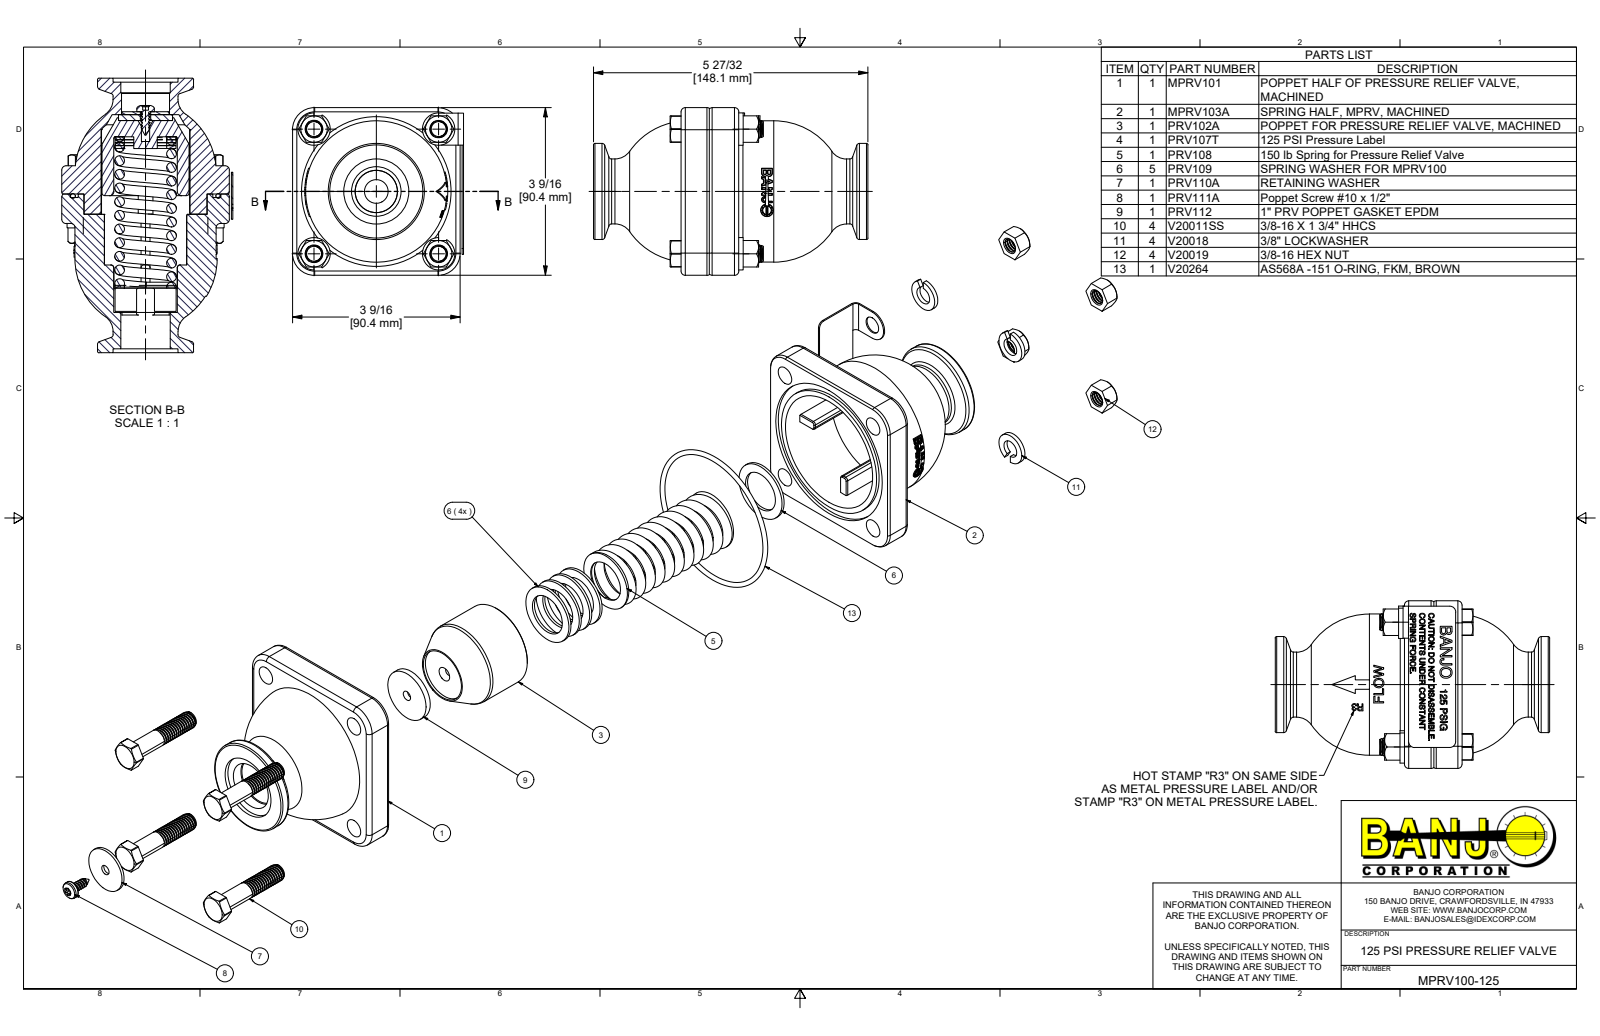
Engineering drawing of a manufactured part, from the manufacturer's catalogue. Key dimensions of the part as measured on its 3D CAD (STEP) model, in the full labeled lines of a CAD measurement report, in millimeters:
Part name (STEP PRODUCT): MPRV100-125; MPRV101; MPRV101X; MPRV103A (+8 more)
STEP written by: Autodesk Inventor 2022 (AUTOMOTIVE_DESIGN)
Units: millimetres
Bodies: 26 solids, 2572 faces (999 planar, 620 cylindrical, 953 other)
Overall size (bounding box): 148.1 × 92.3 × 90.4
Volume: 356 900 mm³ · Surface area: 152 700 mm²
Round holes (diameter × count): ⌀7.8 ×4, ⌀9.8 ×4, ⌀10.3 ×4, ⌀4.4 ×1, ⌀4.6 ×1, ⌀5.6 ×1, ⌀6.5 ×1, ⌀9.7 ×1, ⌀22.9 ×1, ⌀25.9 ×1, ⌀26.7 ×1, ⌀29.1 ×1
Round bosses / shafts (diameter × count): ⌀8.2 ×60, ⌀17.4 ×4, ⌀9.5 ×4, ⌀76.2 ×1, ⌀72.6 ×1, ⌀51.8 ×1, ⌀47 ×1, ⌀32.9 ×1
Partial cylindrical surfaces — rounded edges, fillets, slot ends (radius × count): R0.8 ×28, R1.5 ×24, R2.3 ×16, R4.1 ×8, R0.4 ×6, R0.7 ×6, R8.1 ×4, R11.9 ×4
Main face-to-face distances: 42.8, 47.6, 90.4, 15.2, 15.9, 31.1, 41.2, 49.2, 1.5, 6.4
Hole centre spacings: 47.5, 67.3, 95.1
